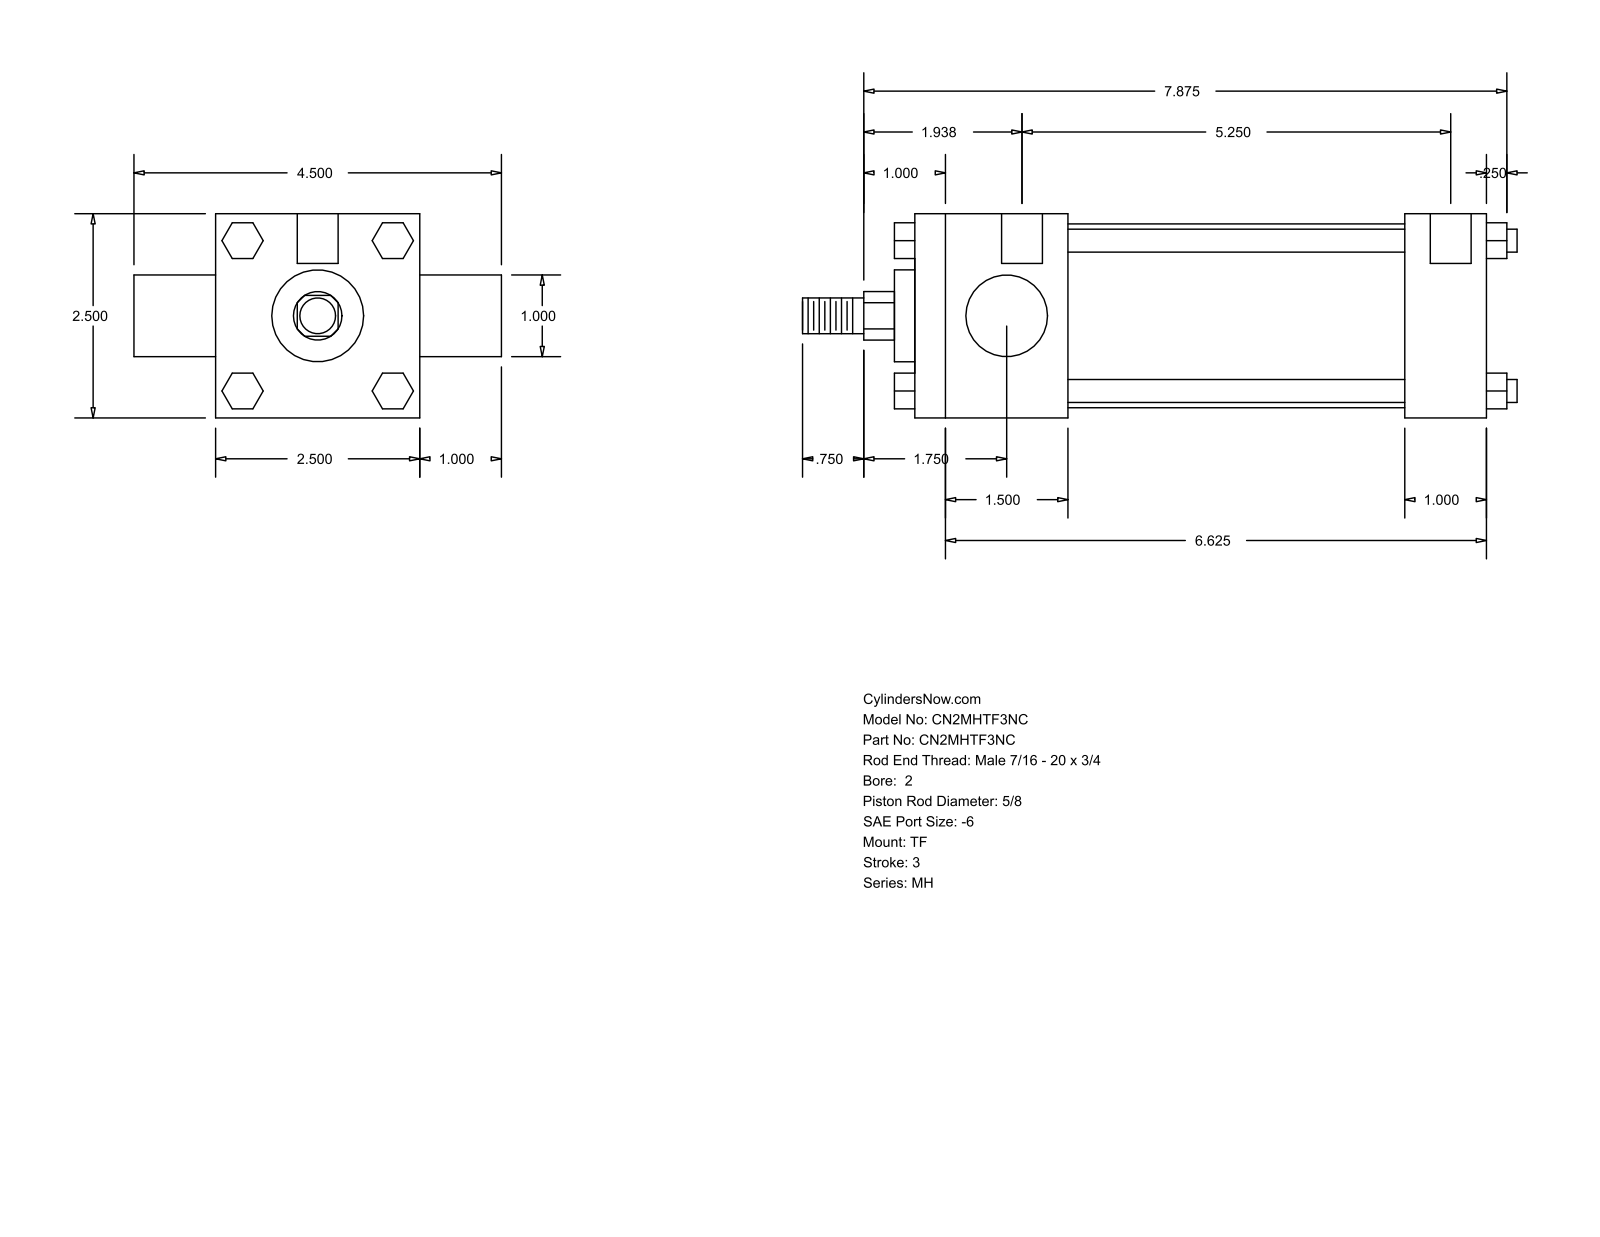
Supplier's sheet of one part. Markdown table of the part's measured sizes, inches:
| quantity | value |
| --- | --- |
| part name | MH_TF__0200_0.625 |
| STEP written by | GSSL Pune (CONFIG_CONTROL_DESIGN) |
| units | inches |
| bodies | 0 solids, 120 faces (92 planar, 28 cylindrical, 0 other) |
| overall size | 8.75 × 4.5 × 2.5 |
| round holes (diameter × count) | 0.219 × 3, 0.5 × 2 |
| round bosses / shafts (diameter × count) | 0.281 × 4, 2.25 × 1, 1.125 × 1, 1 × 1, 0.625 × 1, 0.437 × 1 |
| partial cylindrical surfaces (radius × count) | 0.297 × 1 |
| main face-to-face distances | 2.5, 7, 1, 1.875, 6, 4.125, 5.125, 0.25, 3.5, 7.25 |
| hole center spacings | 0.125, 0.187, 5.25, 5.375, 5.437, 5.563 |
